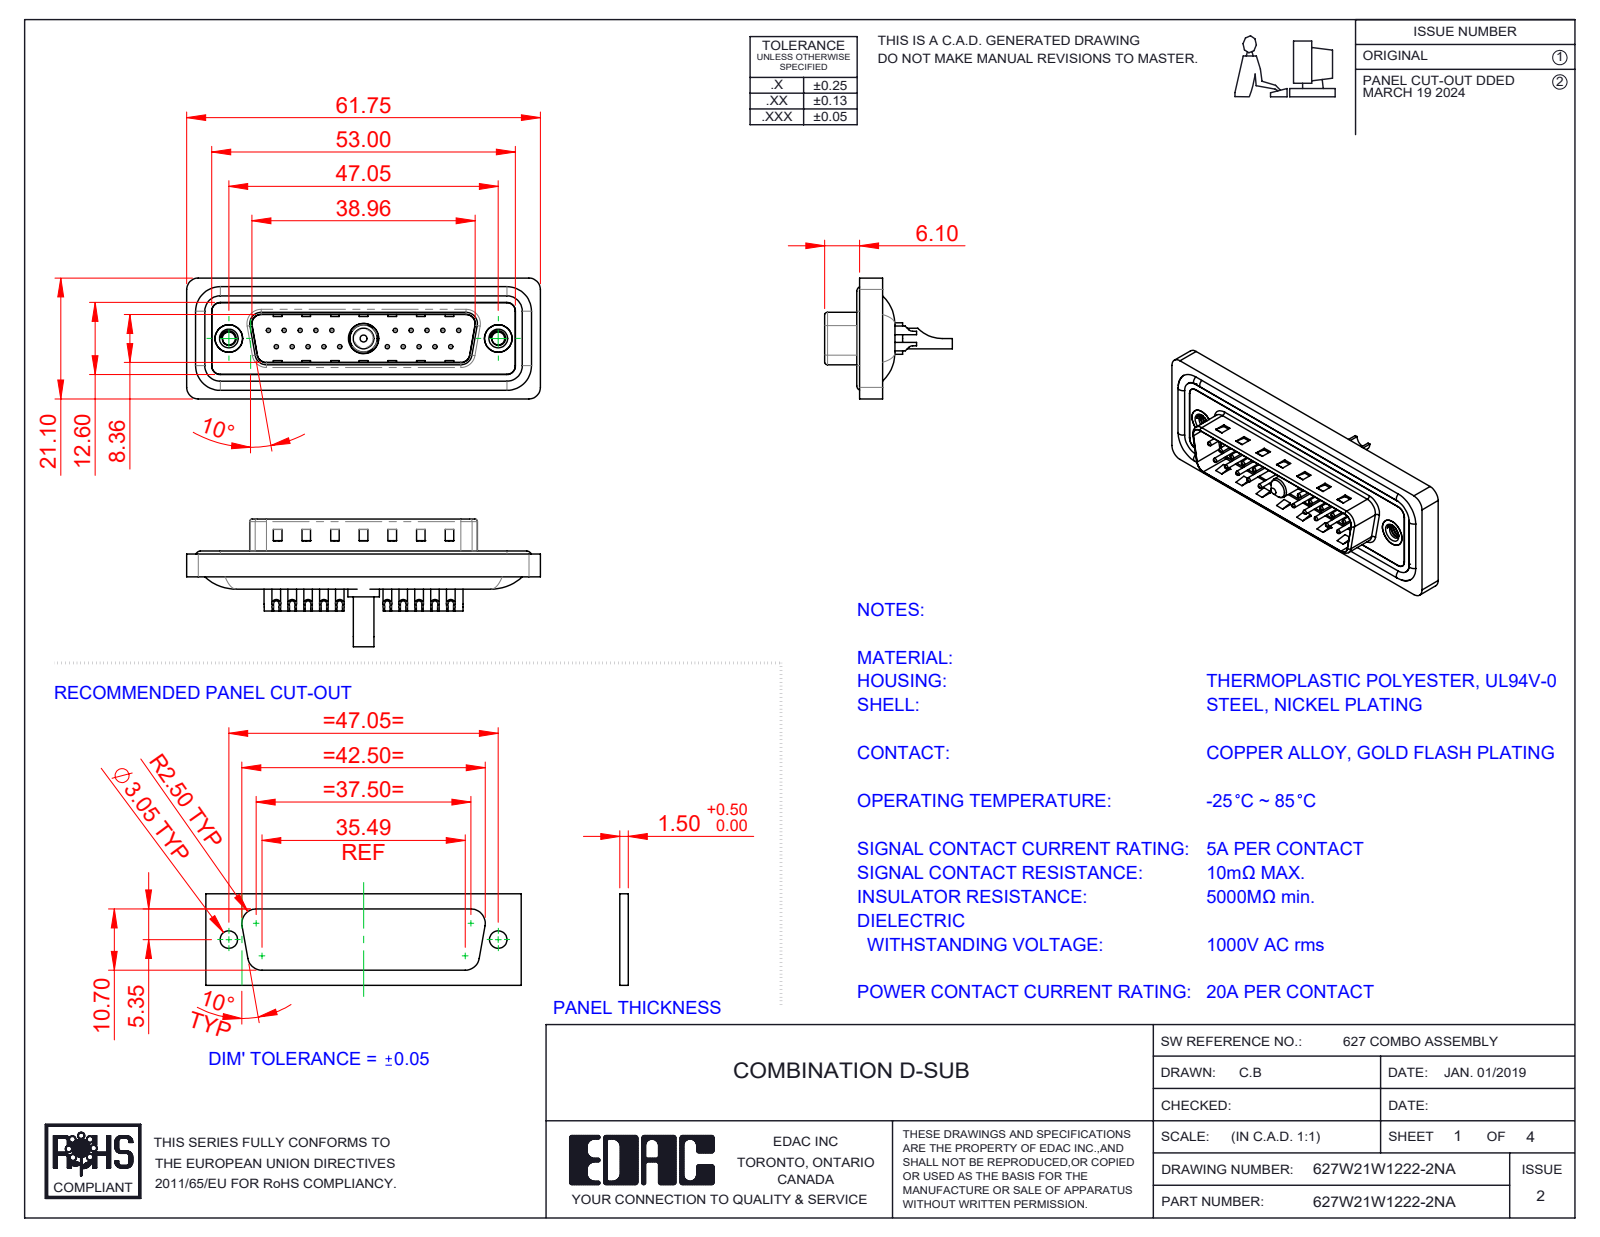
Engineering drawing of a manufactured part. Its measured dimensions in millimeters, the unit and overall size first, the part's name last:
Units: millimetres
Overall size (bounding box): 61.75 × 22.3 × 21.1
Round holes (diameter × count): ⌀0.75 ×20, ⌀1 ×20, ⌀1.6 ×20, ⌀2 ×20, ⌀2.26 ×2, ⌀4 ×2, ⌀4.8 ×2, ⌀5 ×2, ⌀2.7 ×1, ⌀4.85 ×1, ⌀5.3 ×1
Round bosses / shafts (diameter × count): ⌀1.5 ×20, ⌀1.6 ×4, ⌀4.9 ×2, ⌀5.5 ×1, ⌀5.2 ×1, ⌀4.75 ×1, ⌀3.75 ×1, ⌀3.6 ×1
Partial cylindrical surfaces — rounded edges, fillets, slot ends (radius × count): R1.5 ×22, R2 ×18, R0.5 ×8, R1.6 ×8, R1 ×6, R0.25 ×4, R0.6 ×4, R0.65 ×4
Main face-to-face distances: 0.4, 1.5, 1.1, 1.6, 0.5, 3.1, 2.9, 4.1, 0.82, 9.58
Hole centre spacings: 3.16, 2.77, 5.54, 8.31, 5.04, 19.39, 20.97, 22.16
Volume: 7 243 mm³ · Surface area: 12 193 mm²
Bodies: 29 solids, 1267 faces (402 planar, 532 cylindrical, 333 other)
Part name (STEP PRODUCT): 627Combo Shell Front_25 Contacts; 627Combo Waterproof Housing_25 Contacts; 627Combo Housing_21W1; 627Combo Contact Row 2_22 (+5 more)
STEP written by: SolidWorks 2023 (CONFIG_CONTROL_DESIGN)
